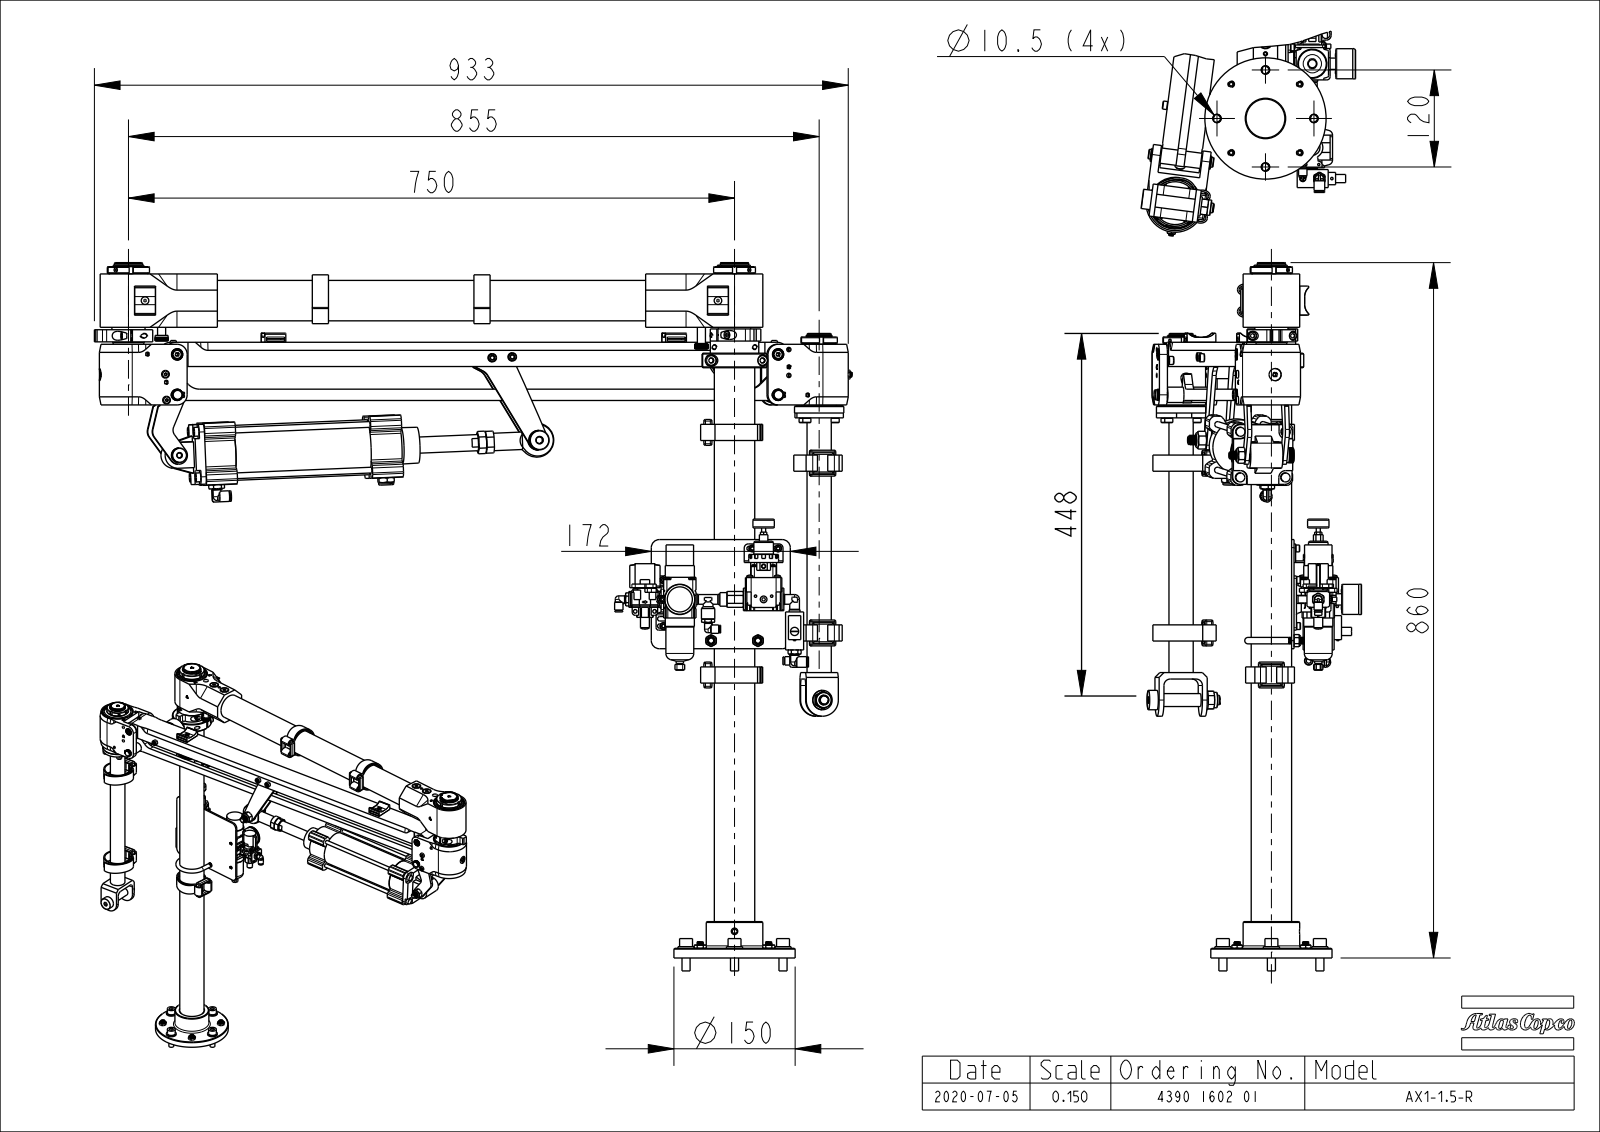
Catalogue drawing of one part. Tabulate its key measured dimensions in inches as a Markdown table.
| quantity | value |
| --- | --- |
| part name | PILLAR_860_NY; BOOM_ARM_750; BEARING_HOUSING; UPPER_PARALLEL (+4 more) |
| STEP written by | CREO PARAMETRIC BY PTC INC, 2022414 (CONFIG_CONTROL_DESIGN) |
| units | inches |
| bodies | 21 solids, 5124 faces (1905 planar, 1963 cylindrical, 1256 other) |
| overall size | 36.911 × 34.488 × 10.479 |
| volume | 452.7 in³ |
| surface area | 2 055 in² |
| round holes (diameter × count) | 0.165 × 31, 0.197 × 14, 0.26 × 10, 0.268 × 10, 0.059 × 8, 0.331 × 6, 0.433 × 6, 0.472 × 6, 0.394 × 5, 0.098 × 4, 0.209 × 4, 0.276 × 4 |
| round bosses / shafts (diameter × count) | 0.394 × 24, 0.315 × 16, 0.472 × 12, 0.236 × 12, 0.63 × 11, 0.945 × 6, 0.787 × 6, 0.276 × 6 |
| partial cylindrical surfaces (radius × count) | 0.079 × 146, 0.157 × 46, 0.008 × 28, 0.059 × 24, 0.394 × 17, 0.118 × 14, 0.197 × 13, 0.591 × 13 |
| main face-to-face distances | 0.118, 1.181, 0.394, 0.787, 1.181, 28.795, 29.976, 1.968, 0.472, 28.323 |
| hole center spacings | 1.969, 1.808, 4.365, 29.528, 1.26, 1.927, 2.06, 2.287 |
